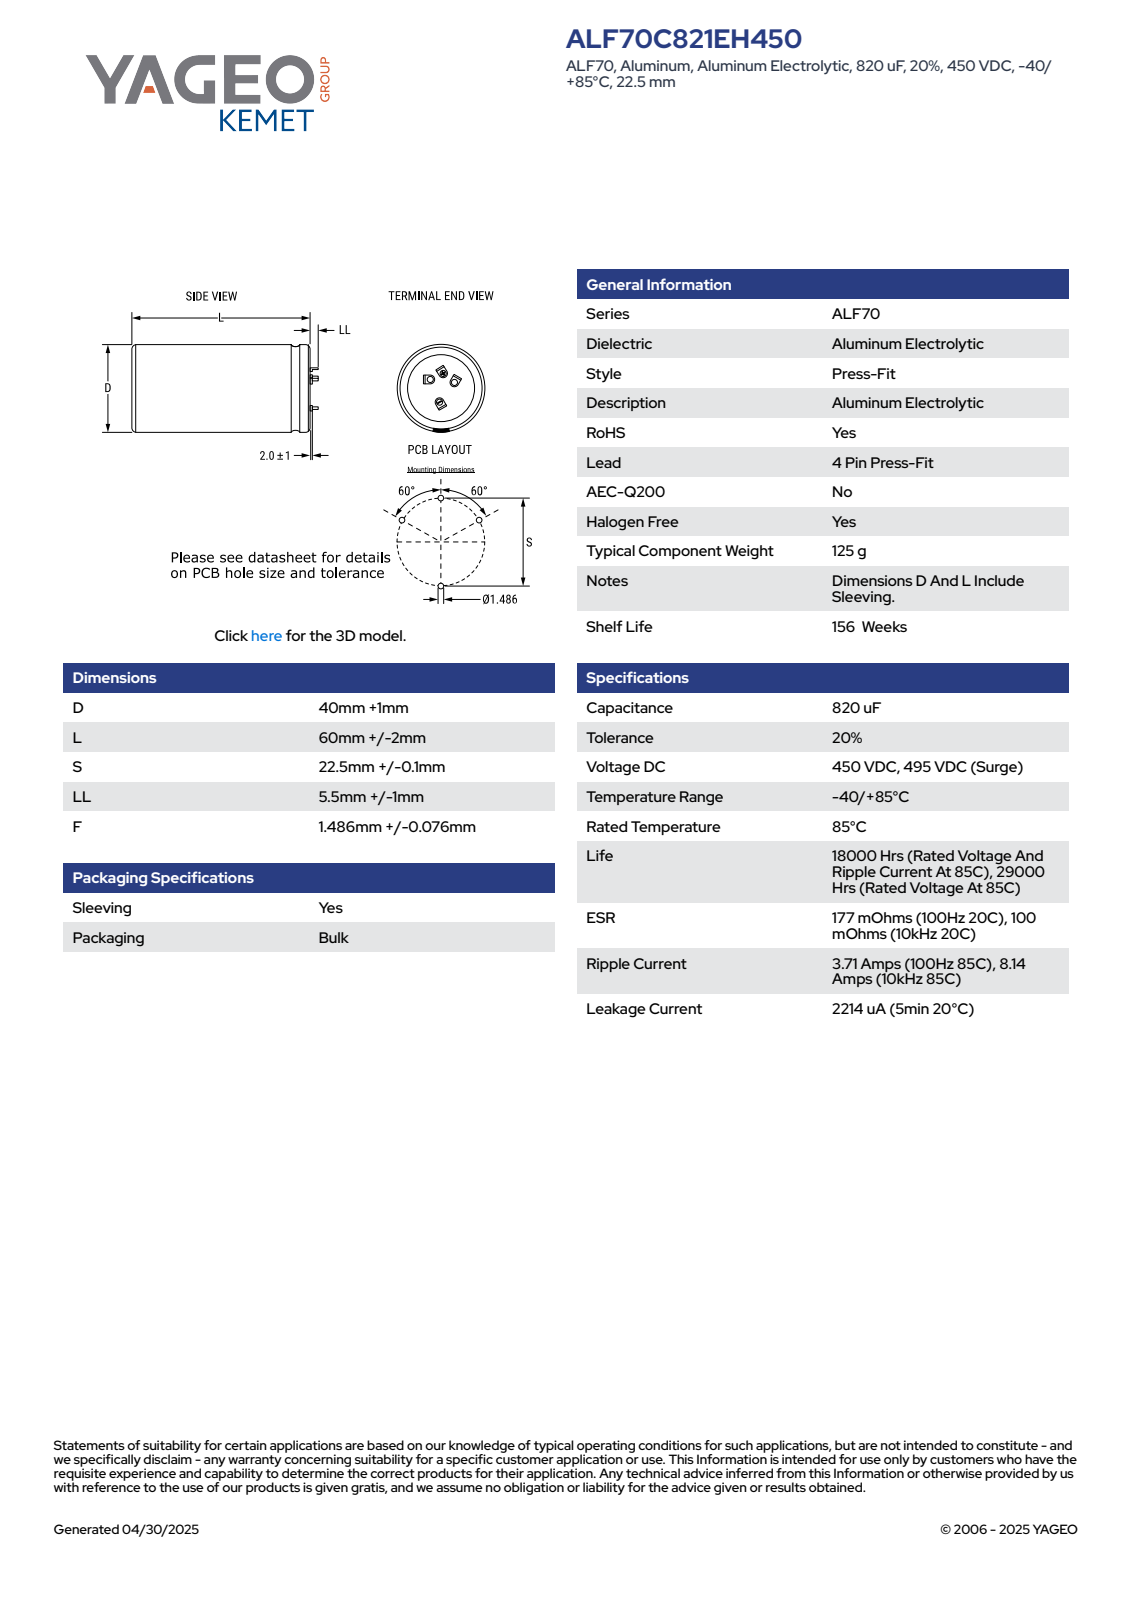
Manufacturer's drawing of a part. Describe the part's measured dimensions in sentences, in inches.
The part is named "CARS_ALF2040C_40X60_D41L62S22.5LL6.5". Its 3-D file was written by "SolidWorks 2014 (AUTOMOTIVE_DESIGN)". It is 6 solids with 333 faces: 139 planar, 138 cylindrical and 56 other. Overall it measures 2.701 by 1.614 by 1.614 inches. Its volume is 4.979 cubic inches and its surface area 16.93 square inches. Round bosses or shafts: 4 of diameter 0.138, 1 of diameter 1.614. Partial cylindrical surfaces (rounded edges, fillets, slot ends): 50 of radius 0.006, 8 of radius 0.004, 8 of radius 0.017, 3 of radius 0.098, 1 of radius 0.099. The main face-to-face distances are 2.441, 2.441, 0.031, 0.197, 0.118, 0.119, 2.559, 0.197, 0.26, 0.142.
